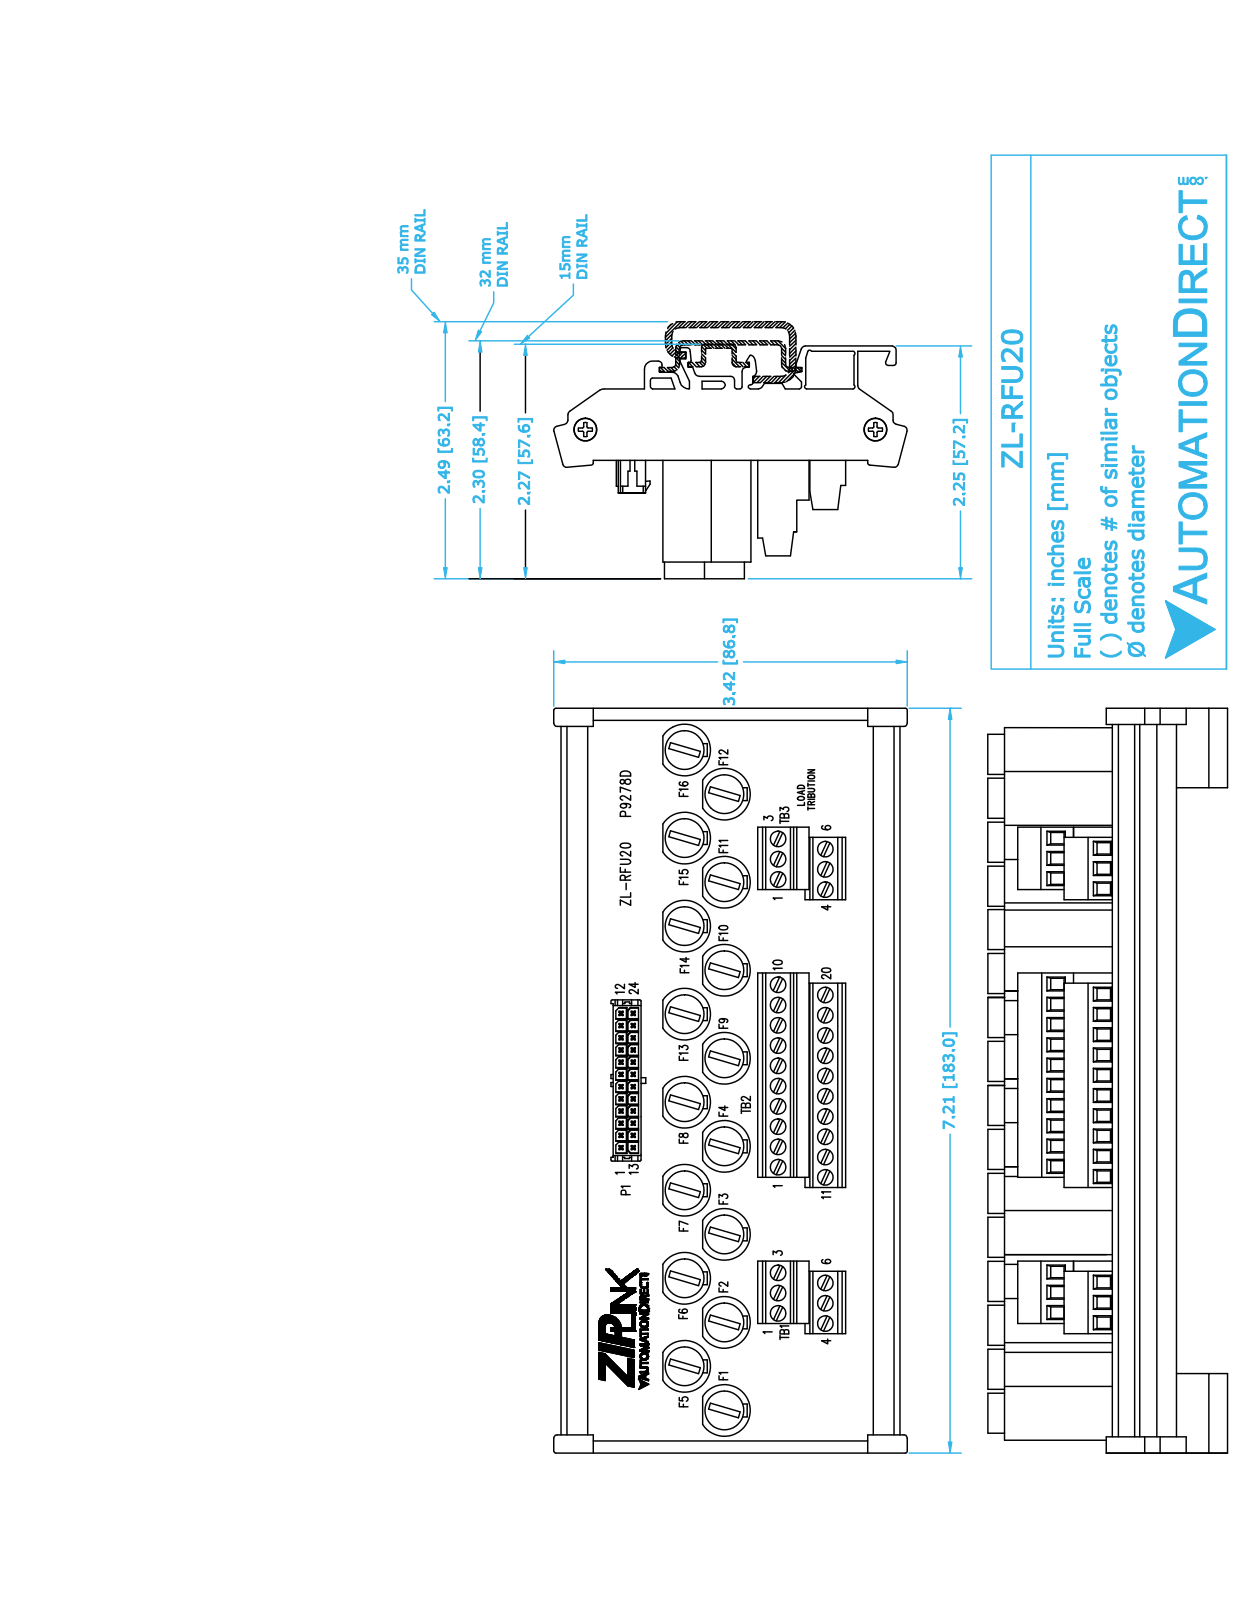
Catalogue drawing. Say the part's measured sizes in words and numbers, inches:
The part is named "ZL-RFU20". Its 3-D file was written by "SolidWorks 2014 (AUTOMOTIVE_DESIGN)". It is 1 solid with 1413 faces: 1144 planar, 229 cylindrical and 40 other. Overall it measures 7.266 by 3.42 by 2.38 inches. Its volume is 11.15 cubic inches and its surface area 171.9 square inches. Round holes: 32 of diameter 0.15, 2 of diameter 0.225. Round bosses or shafts: 8 of diameter 0.38, 8 of diameter 0.36, 8 of diameter 0.34, 8 of diameter 0.32, 2 of diameter 0.205. Partial cylindrical surfaces (rounded edges, fillets, slot ends): 41 of radius 0.015, 10 of radius 0.03. The main face-to-face distances are 0.434, 0.491, 0.057, 0.137, 0.571, 0.628, 0.03, 0.658, 0.52, 0.087. The hole center spacings are 0.487, 0.2, 0.563, 0.4, 0.691, 1.2, 1.385, 1.4.
